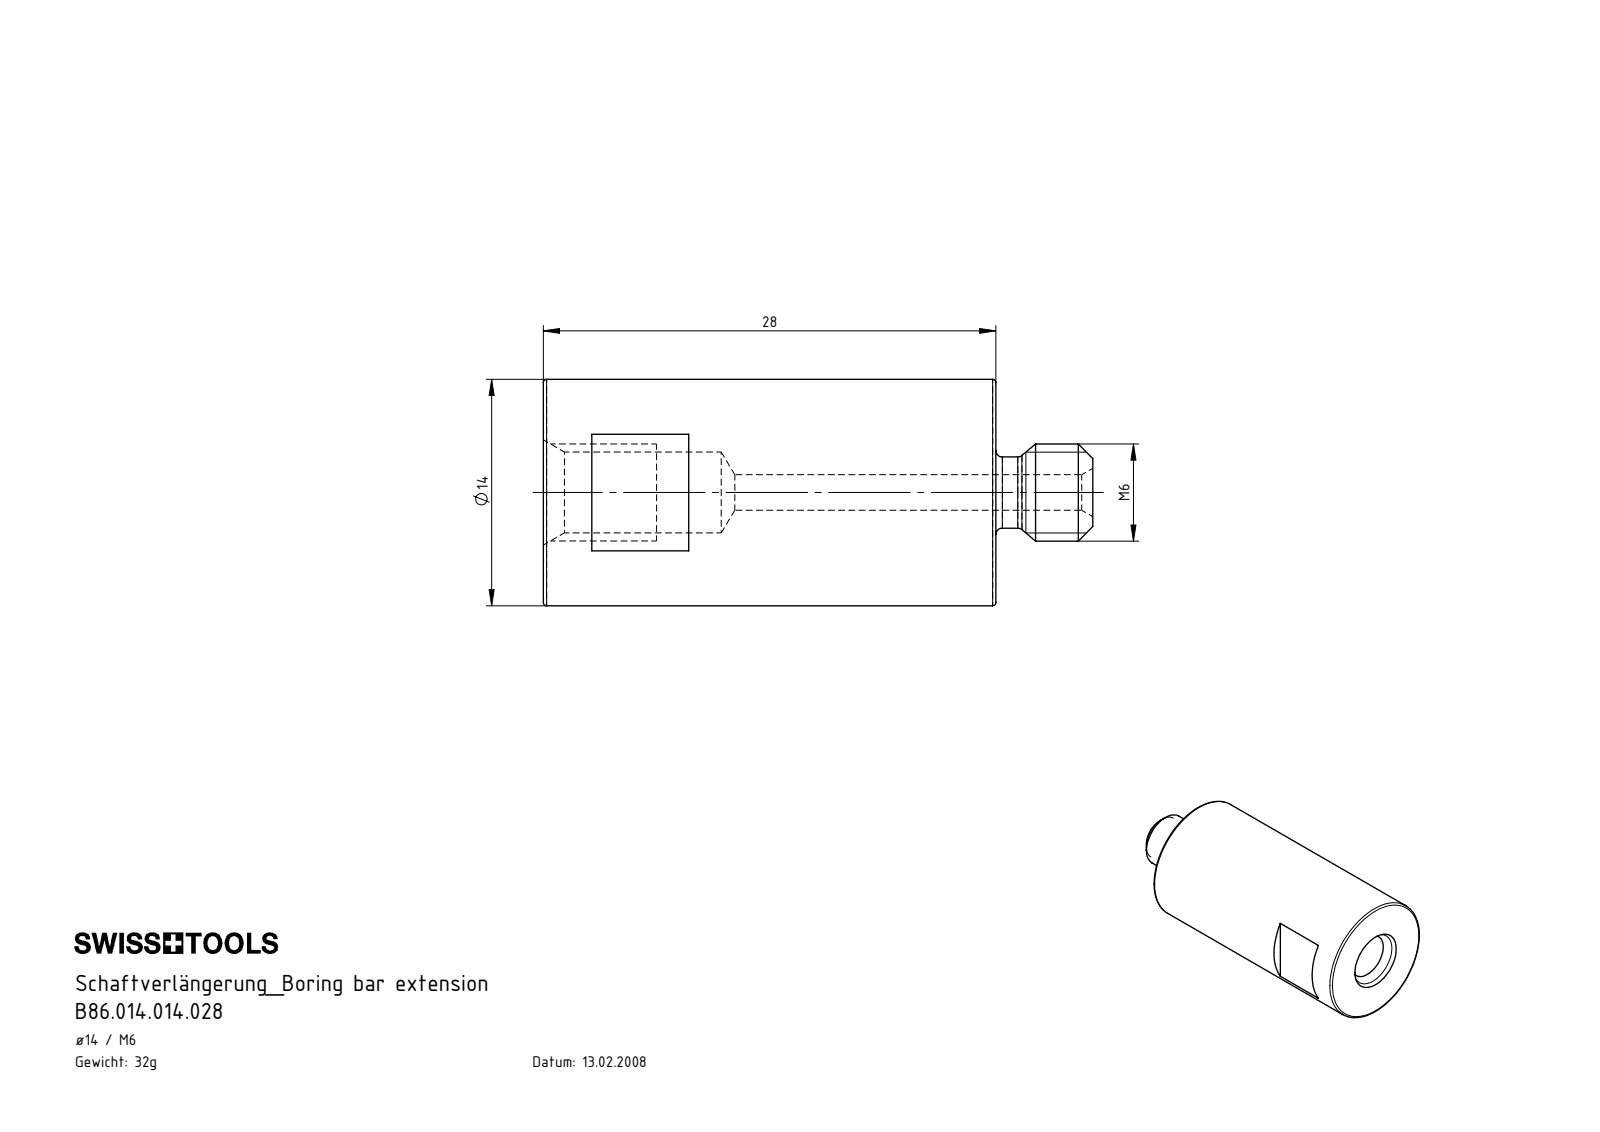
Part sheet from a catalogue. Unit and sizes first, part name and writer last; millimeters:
Units: millimetres
Overall size (bounding box): 34 × 14 × 14
Round holes (diameter × count): ⌀2.2 ×1, ⌀5 ×1
Round bosses / shafts (diameter × count): ⌀14 ×1, ⌀6 ×1, ⌀4.4 ×1
Main face-to-face distances: 28, 12, 25, 6, 3, 19, 9, 31, 34
Volume: 4 069 mm³ · Surface area: 1 967 mm²
Bodies: 1 solid, 37 faces (9 planar, 10 cylindrical, 18 other)
Part name (STEP PRODUCT): B86.014.014.028
STEP written by: SolidWorks 2022 (CONFIG_CONTROL_DESIGN)
